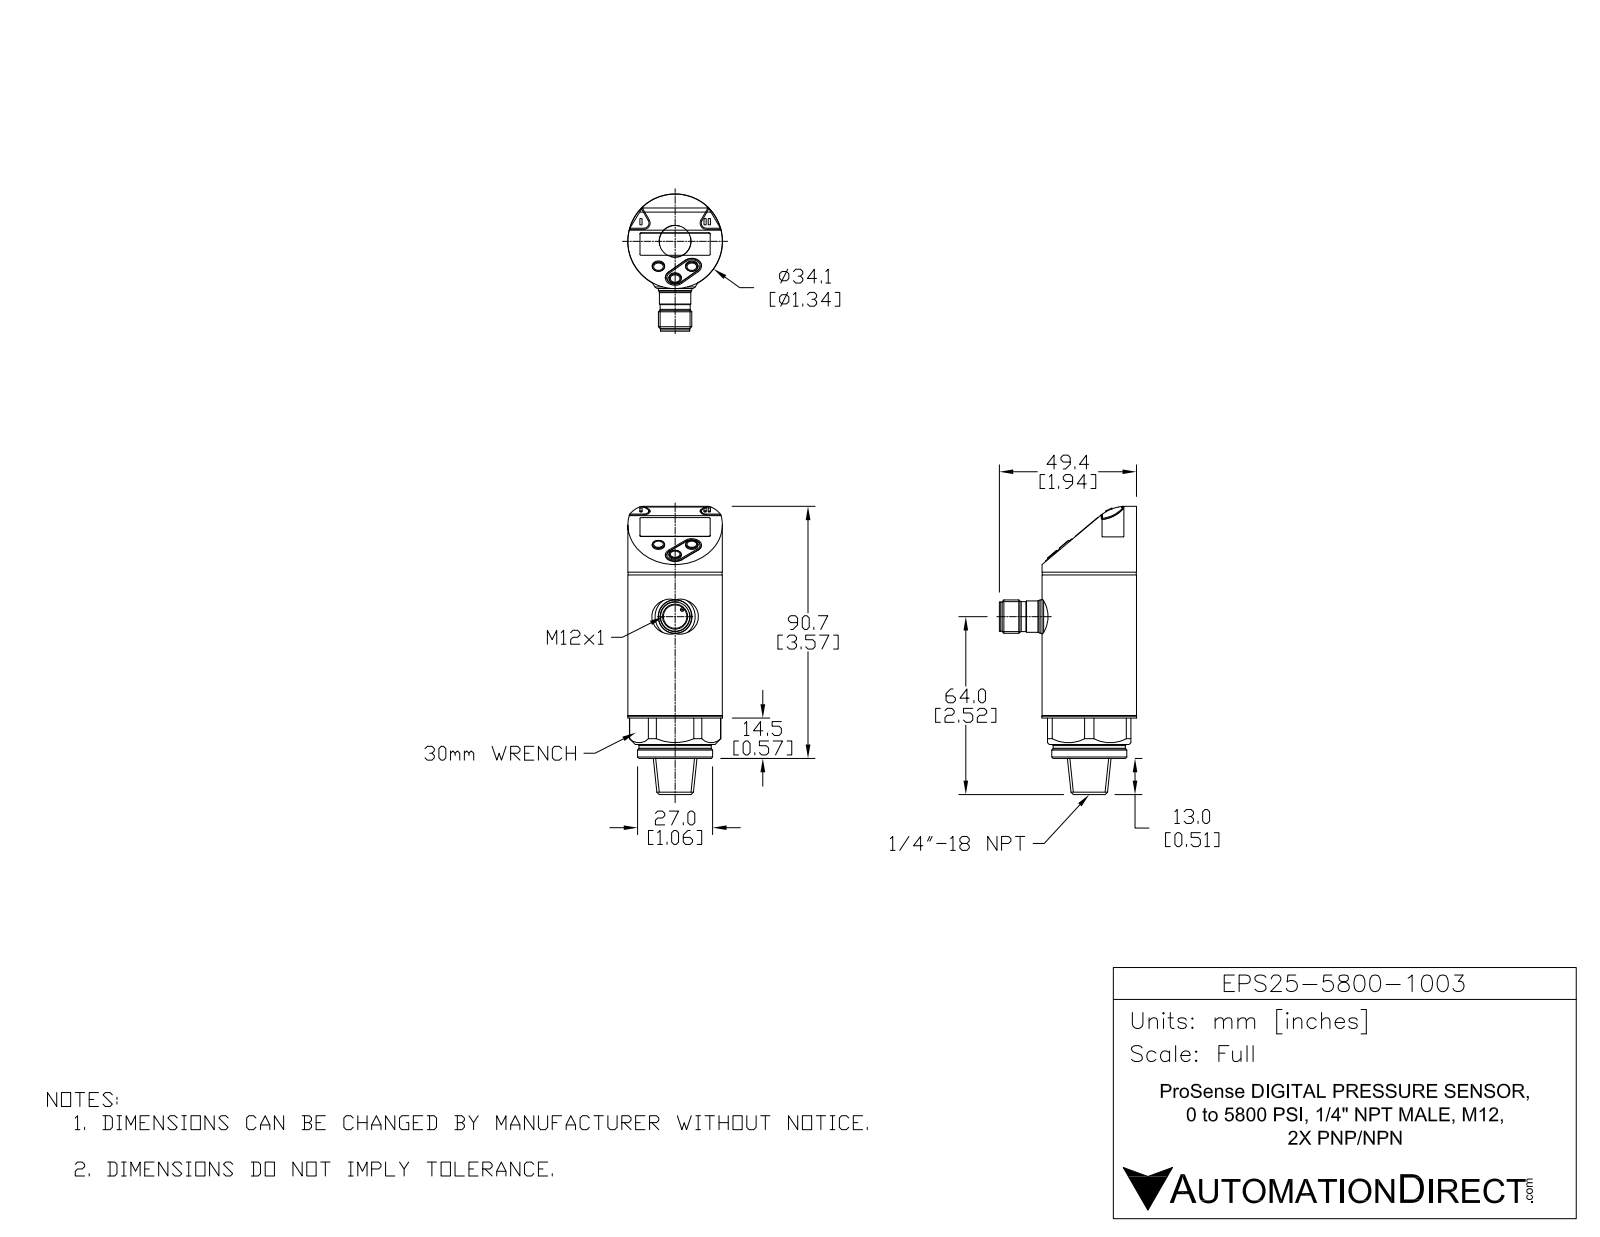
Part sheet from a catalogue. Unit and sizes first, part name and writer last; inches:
Units: inches
Overall size (bounding box): 4.083 × 1.945 × 1.343
Round holes (diameter × count): ⌀0.165 ×1, ⌀0.333 ×1
Round bosses / shafts (diameter × count): ⌀0.055 ×4, ⌀0.039 ×4, ⌀1.343 ×1, ⌀1.339 ×1, ⌀1.331 ×1, ⌀1.063 ×1, ⌀1.024 ×1, ⌀0.472 ×1
Partial cylindrical surfaces — rounded edges, fillets, slot ends (radius × count): R0.071 ×2, R0.087 ×2, R0.118 ×2, R0.138 ×2, R0.591 ×2, R0.024 ×1, R0.268 ×1, R0.647 ×1
Main face-to-face distances: 0.027, 0.453, 0.48, 0.42, 0.059, 0.394, 0.079, 0.098, 0.551, 0.157
Volume: 4.406 in³ · Surface area: 33.12 in²
Bodies: 11 solids, 370 faces (207 planar, 84 cylindrical, 79 other)
Part name (STEP PRODUCT): EPS25-5800-1003
STEP written by: SolidWorks 2016 (AUTOMOTIVE_DESIGN)
